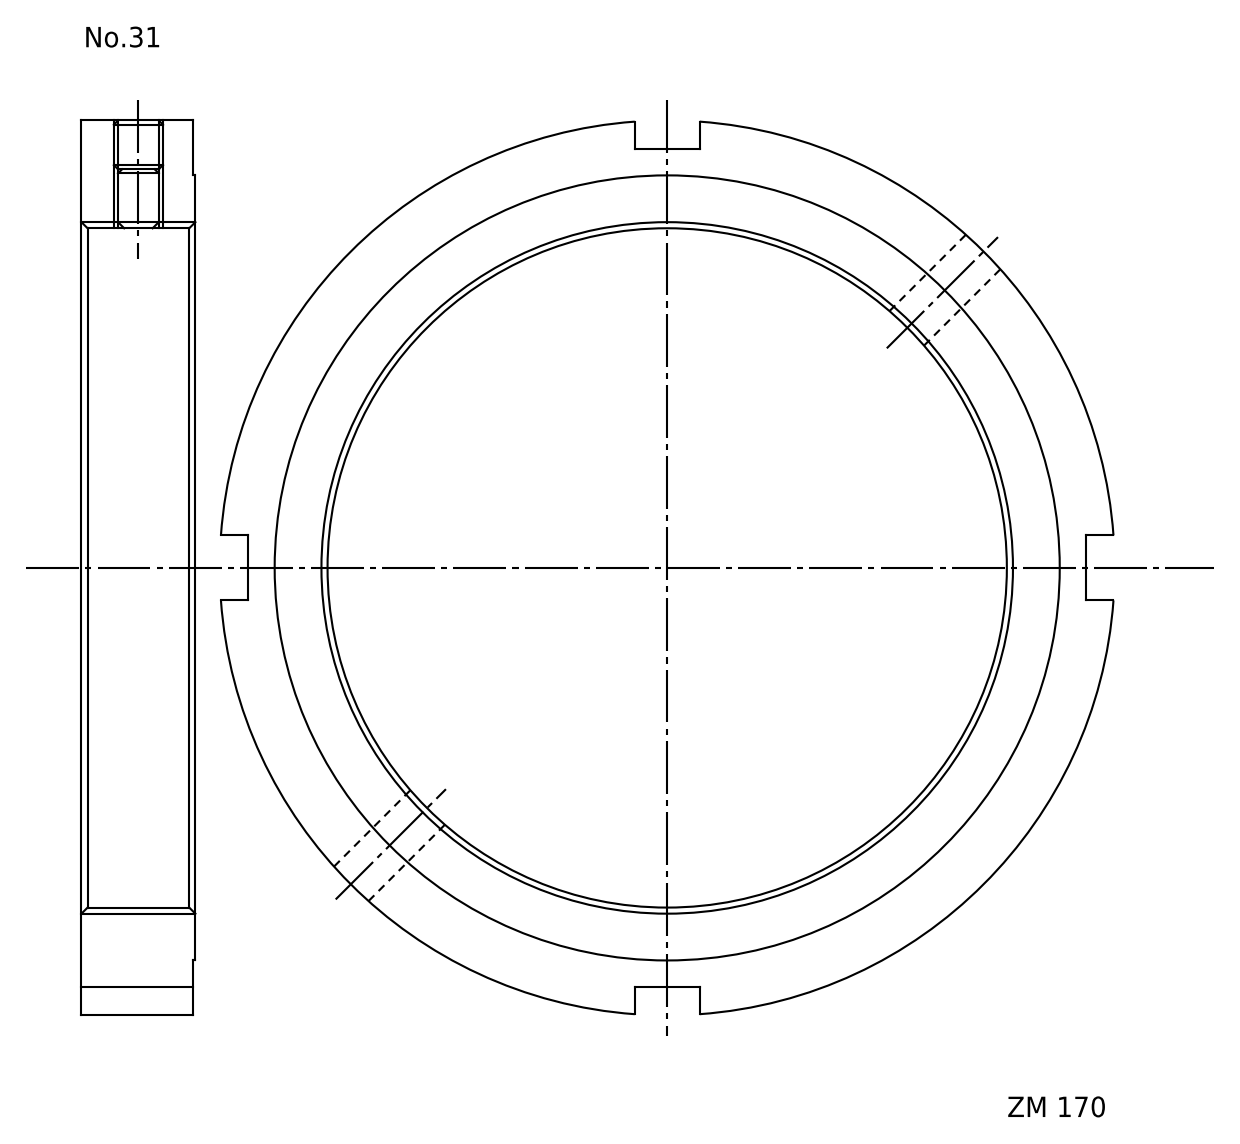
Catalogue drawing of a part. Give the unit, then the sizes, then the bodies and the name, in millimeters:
Units: millimetres
Overall size (bounding box): 219.42 × 219.42 × 28
Round holes (diameter × count): ⌀10.11 ×2, ⌀170 ×1
Round bosses / shafts (diameter × count): ⌀220 ×1, ⌀193 ×1
Main face-to-face distances: 27.5, 0.5, 28, 95, 111, 206, 16
Volume: 408 289 mm³ · Surface area: 66 753 mm²
Bodies: 1 solid, 23 faces (15 planar, 8 cylindrical, 0 other)
Part name (STEP PRODUCT): FKD ZM170
STEP written by: Autodesk Inventor 2011 (AUTOMOTIVE_DESIGN)
